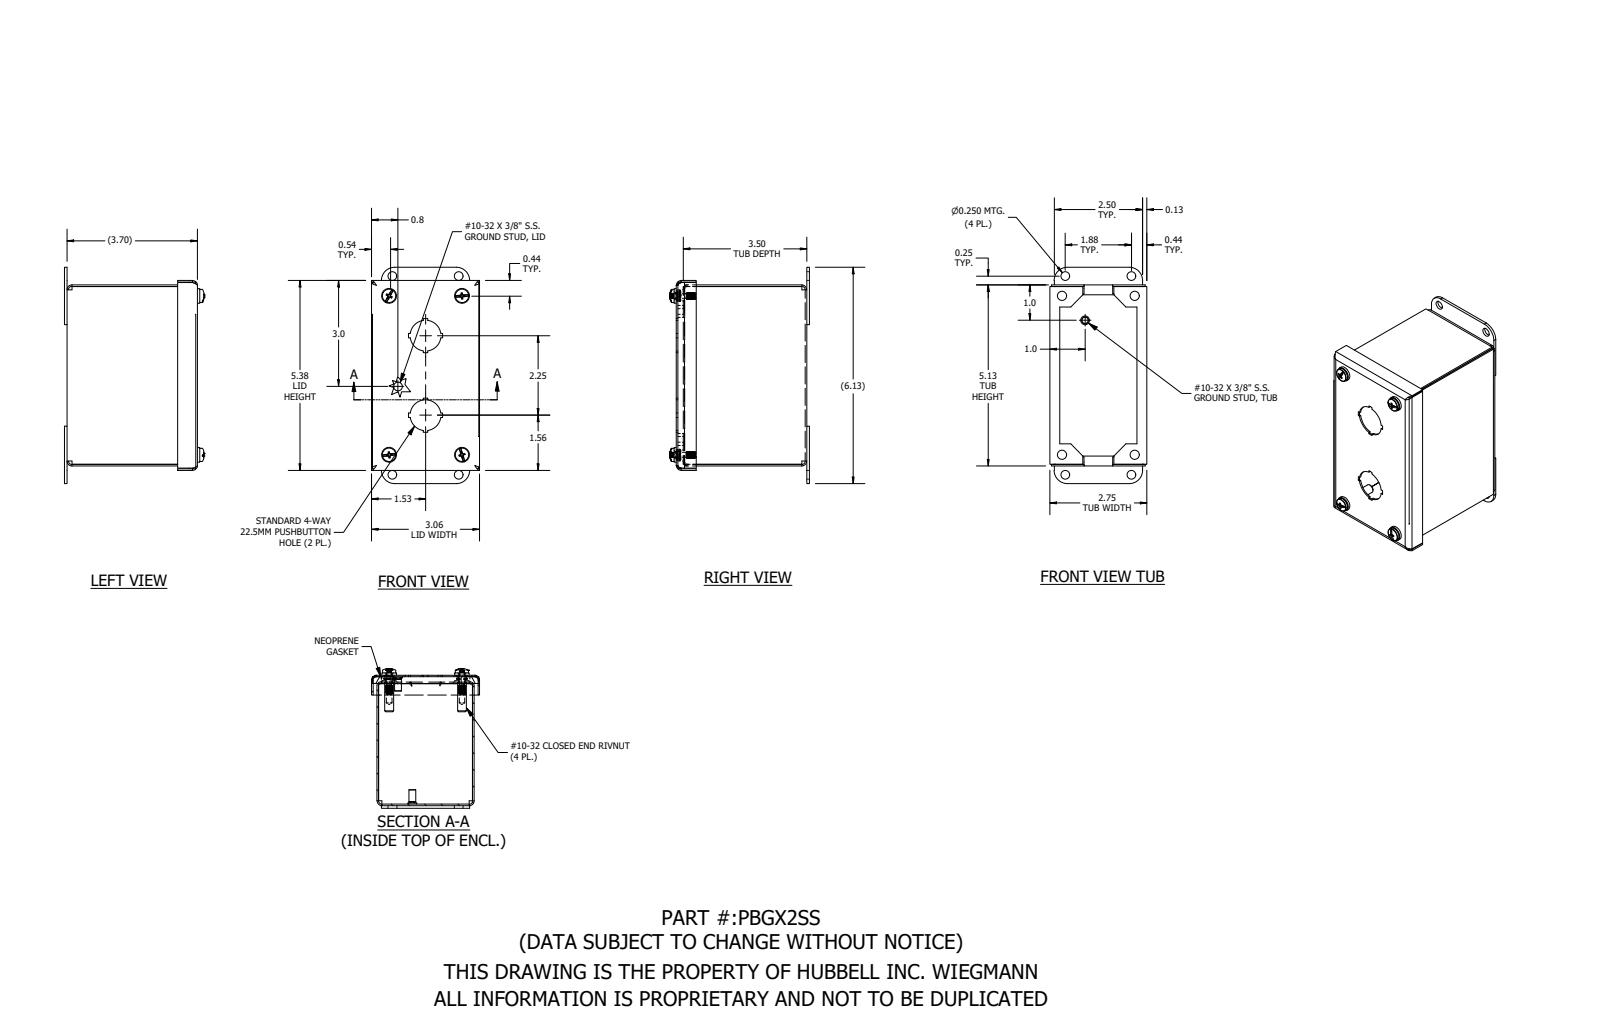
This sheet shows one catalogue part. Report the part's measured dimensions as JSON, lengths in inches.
{"part_name": "PBGX2SS", "step_written_by": "SolidWorks 2021 (AUTOMOTIVE_DESIGN)", "units": "inches", "bodies": {"solids": 20, "faces": 744, "planar": 340, "cylindrical": 252, "other": 152}, "overall_size": [6.125, 3.954, 3.063], "volume_in3": 6.52, "surface_area_in2": 239.3, "round_holes": [[0.156, 4], [0.196, 4], [0.25, 4], [0.257, 4], [0.281, 4], [0.313, 4], [0.133, 2], [0.175, 2], [0.175, 2], [0.875, 2]], "round_bosses_or_shafts": [[0.406, 4], [0.318, 4], [0.248, 4], [0.186, 4], [0.141, 4], [0.14, 4], [0.375, 3], [0.25, 2]], "partial_cylinders_radius": [[0.094, 8], [0.139, 8], [0.063, 4], [0.375, 4], [0.108, 3], [0.107, 1]], "face_to_face_distances": [0.045, 0.045, 3.65, 2.705, 2.75, 2.66, 2.705, 3.695, 3.605, 5.035], "hole_center_spacings": [5.063, 3.567, 4.048, 0.059, 0.565, 0.57, 0.57, 1.526]}
